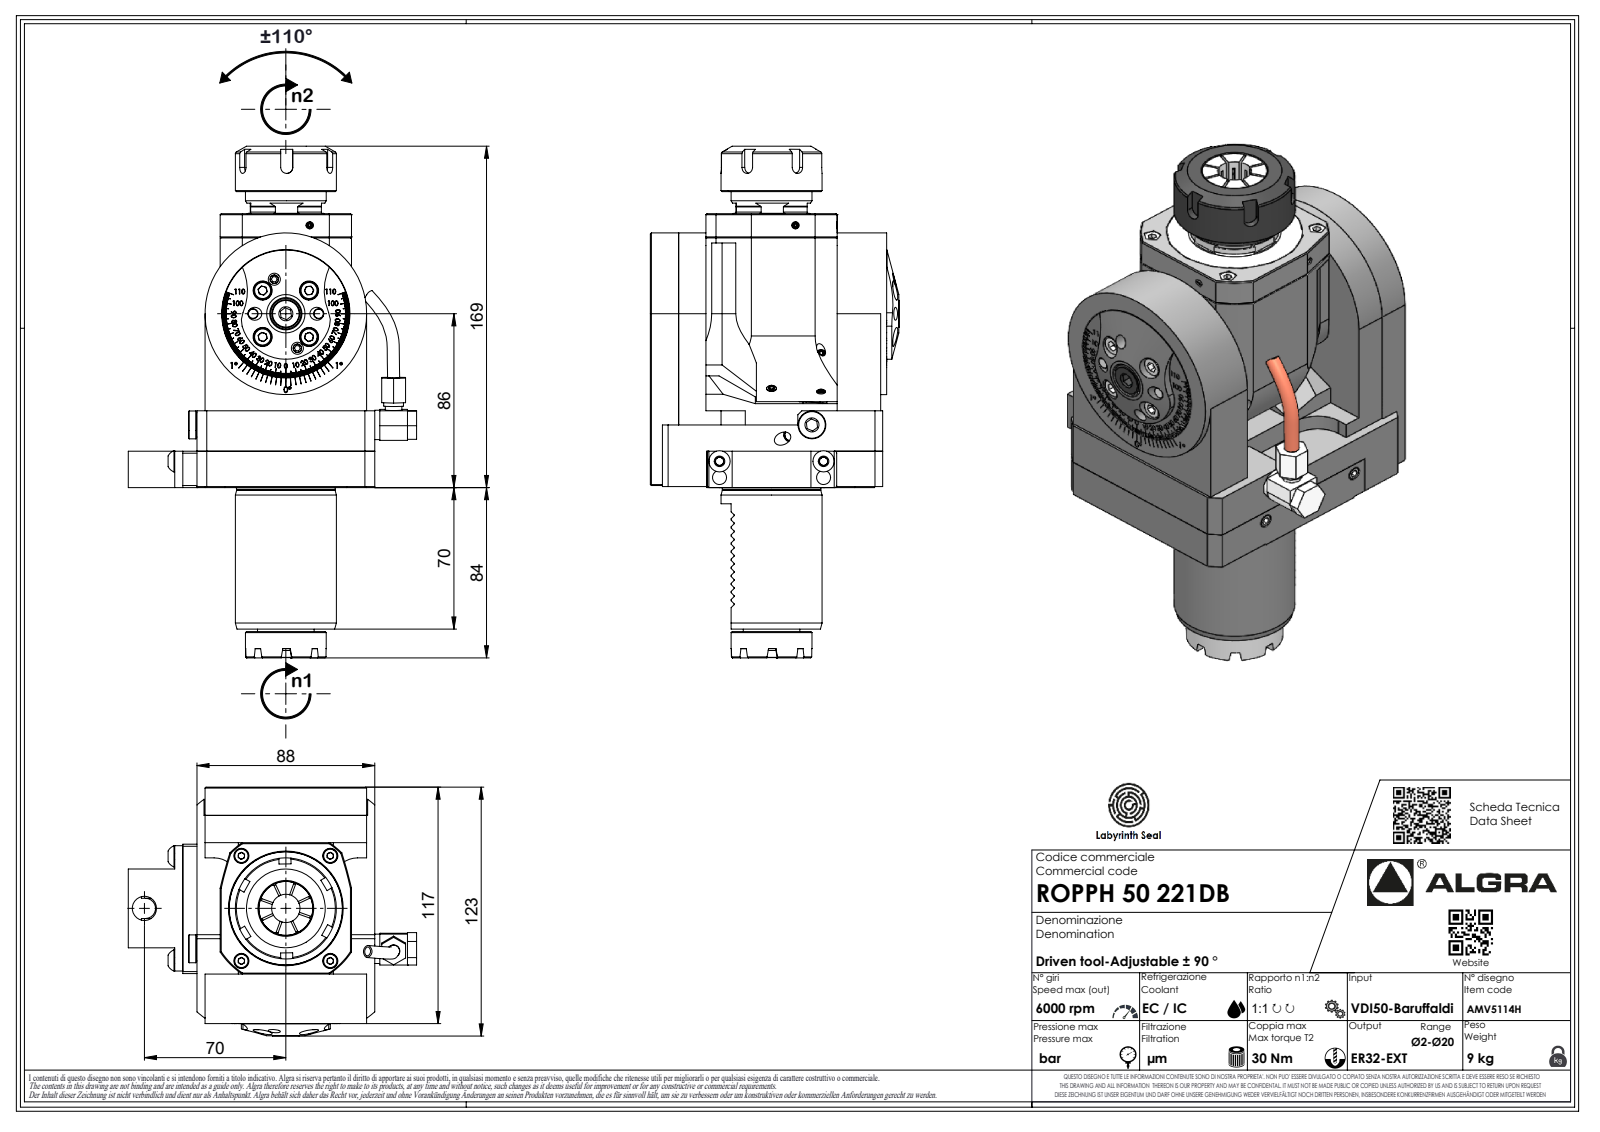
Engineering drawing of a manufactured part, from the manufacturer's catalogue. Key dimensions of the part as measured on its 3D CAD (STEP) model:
Part name (STEP PRODUCT): ROPPH50221DB
STEP written by: SolidWorks 2023 (AUTOMOTIVE_DESIGN)
Units: millimetres
Bodies: 1 solid, 690 faces (429 planar, 129 cylindrical, 132 other)
Overall size (bounding box): 253.16 × 142.7 × 123
Volume: 1 276 000 mm³ · Surface area: 116 831 mm²
Round holes (diameter × count): ⌀2.1 ×1, ⌀44.2 ×1, ⌀48.2 ×1, ⌀52.2 ×1, ⌀56.2 ×1
Round bosses / shafts (diameter × count): ⌀80 ×1, ⌀56 ×1, ⌀52 ×1, ⌀50 ×1, ⌀48.7 ×1, ⌀48 ×1, ⌀44 ×1, ⌀40 ×1
Partial cylindrical surfaces — rounded edges, fillets, slot ends (radius × count): R0.2 ×16, R0.3 ×12, R0.33 ×7, R0.52 ×7, R3.7 ×7, R3 ×5, R1 ×4, R10 ×2
Main face-to-face distances: 4, 65, 84, 0.5, 76.5, 11.5, 22.5, 87.5, 7.5, 72.5
